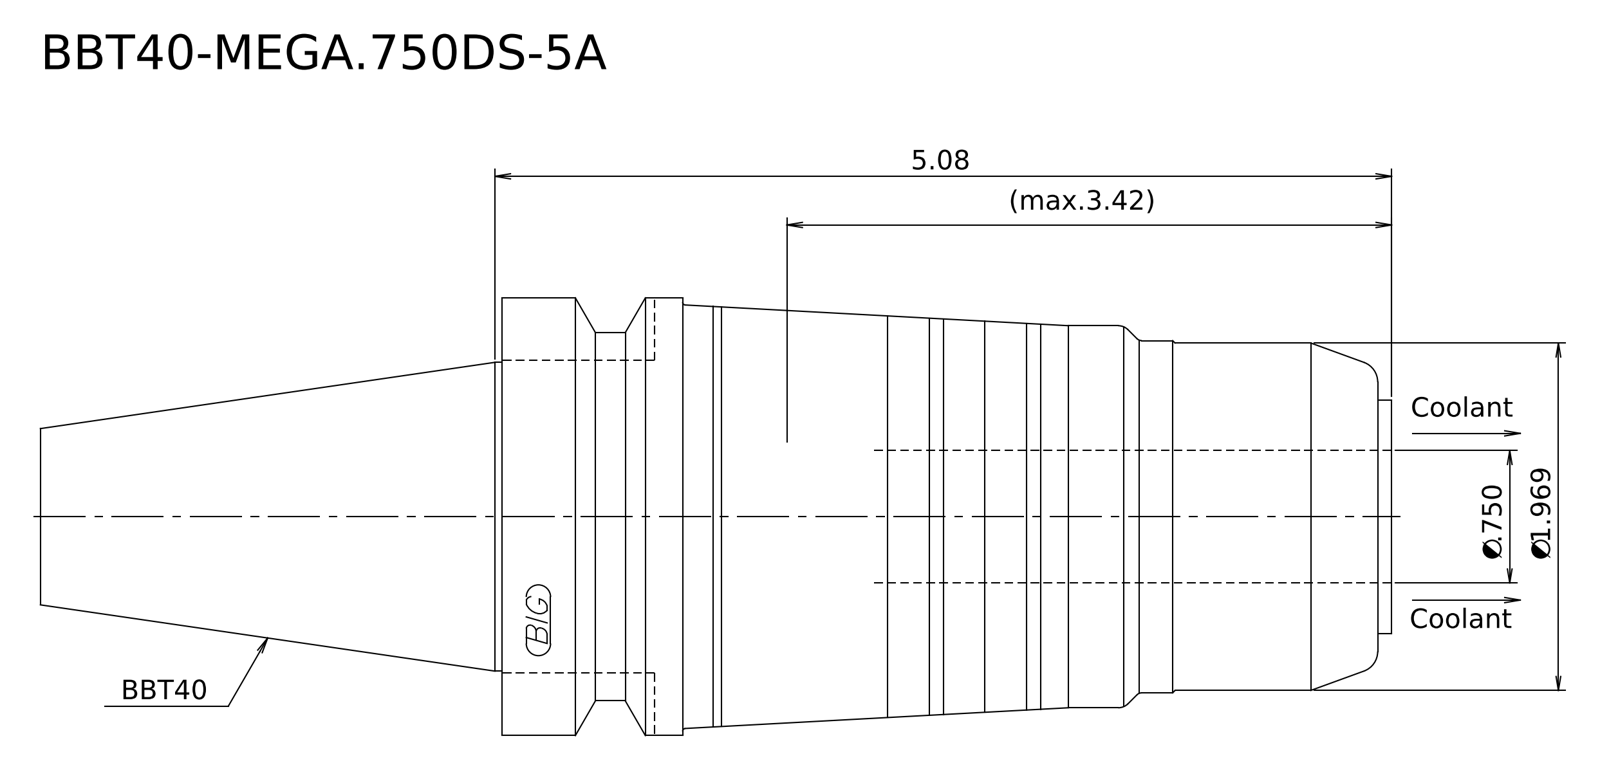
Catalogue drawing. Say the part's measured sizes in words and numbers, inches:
Its 3-D file was written by "Kubotek KeyCreator 2011 V10.0.2 (22737) (automotive_design)". It is 1 solid with 22 faces: 5 planar, 8 cylindrical and 9 other. Overall it measures 7.654 by 2.48 by 2.48 inches. Its volume is 23.04 cubic inches and its surface area 53.74 square inches. Round bosses or shafts: 1 of diameter 2.48, 1 of diameter 2.165, 1 of diameter 2.087, 1 of diameter 1.996, 1 of diameter 1.969, 1 of diameter 1.75, 1 of diameter 1.323. The main face-to-face distances are 5.039, 0.079, 4.961, 7.654, 7.575, 2.614, 4.016, 3.937, 1.024, 3.638.
